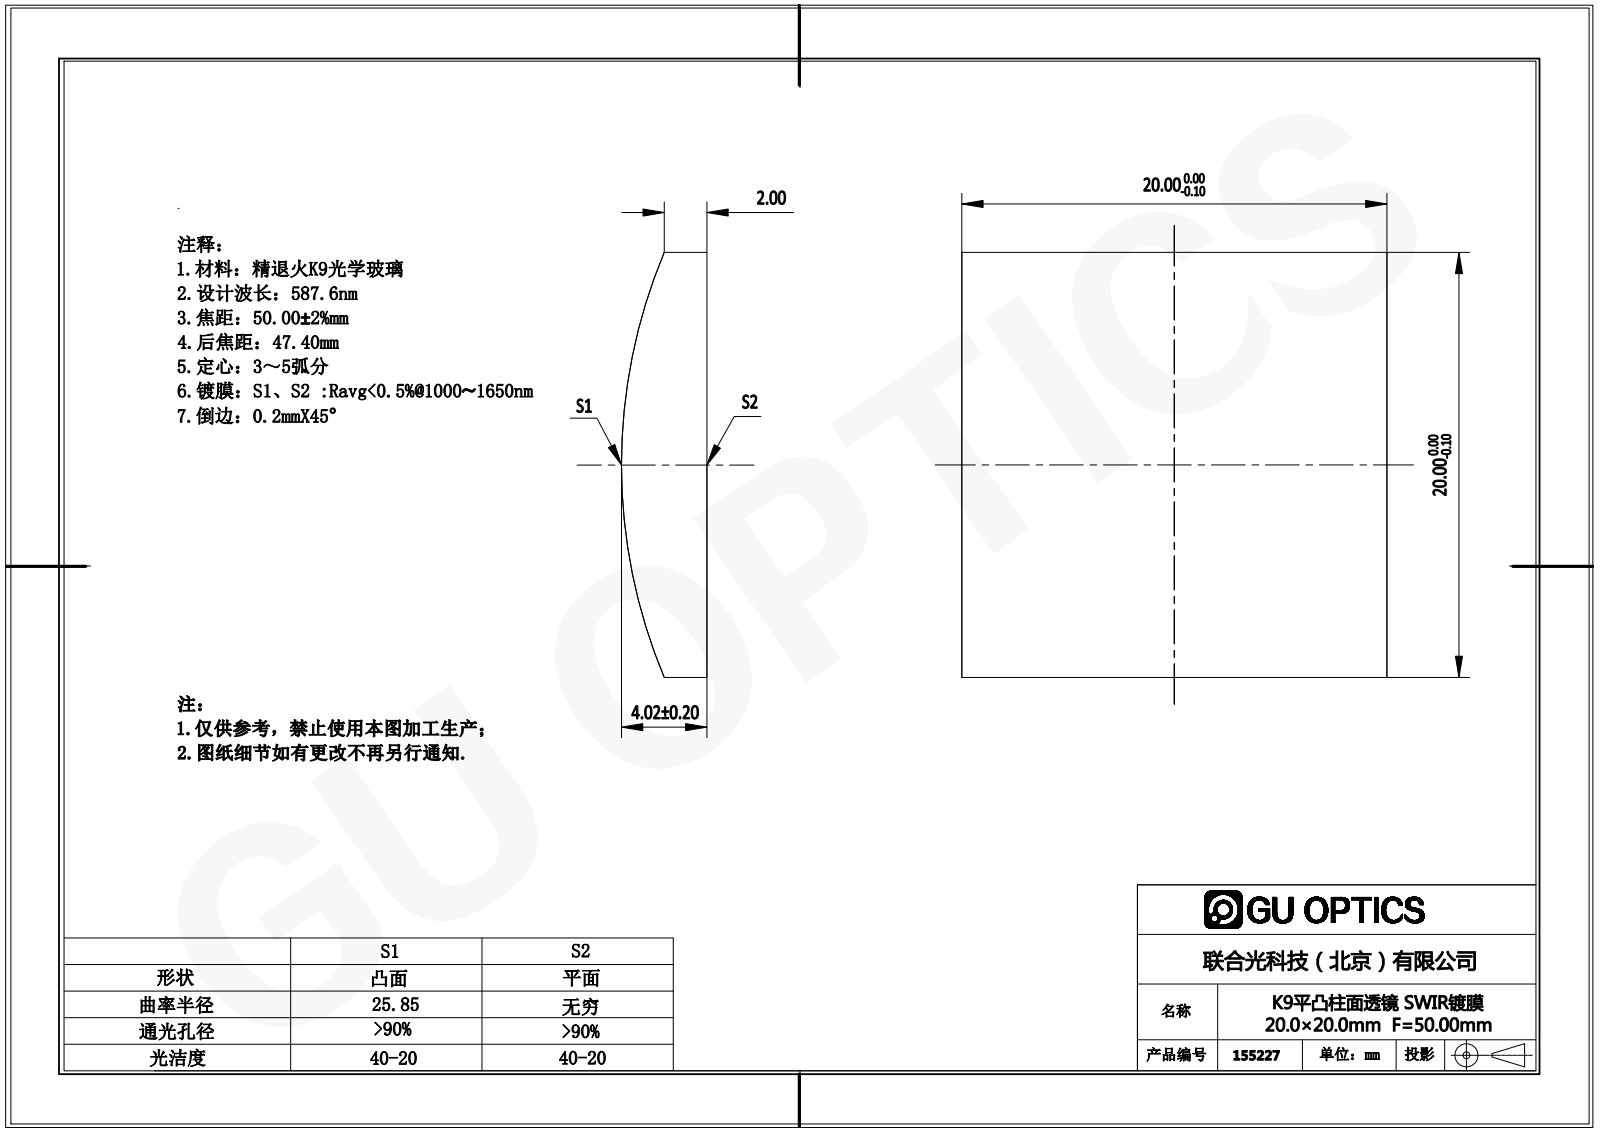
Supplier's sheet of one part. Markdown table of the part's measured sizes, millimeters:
| quantity | value |
| --- | --- |
| part name | 155029 |
| STEP written by | SolidWorks 2016 (AUTOMOTIVE_DESIGN) |
| units | millimeters |
| bodies | 1 solid, 6 faces (5 planar, 1 cylindrical, 0 other) |
| overall size | 20 × 20 × 4.02 |
| volume | 1 344 mm³ |
| surface area | 1 025 mm² |
| partial cylindrical surfaces (radius × count) | 25.85 × 1 |
| main face-to-face distances | 20 |
